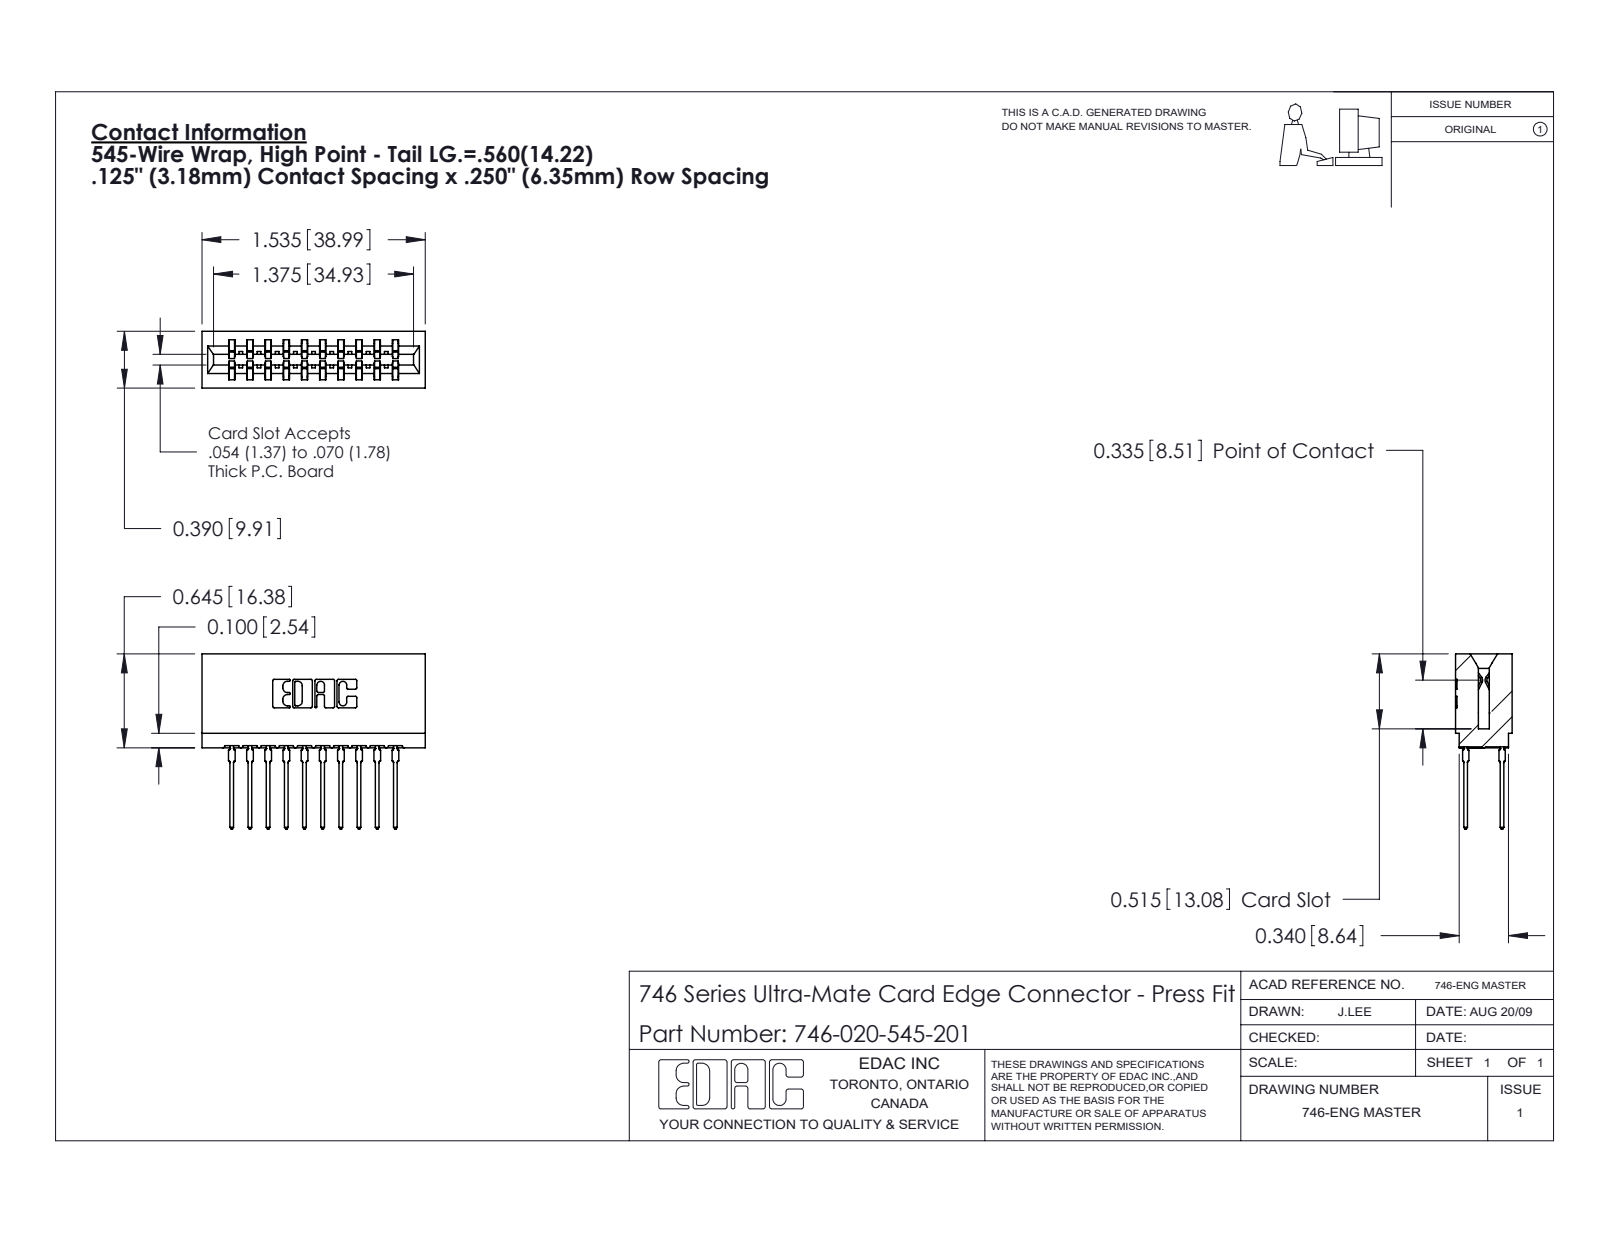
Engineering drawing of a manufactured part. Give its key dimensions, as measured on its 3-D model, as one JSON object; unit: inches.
{"part_name": "746-020-545-201; 746-292-001_545; 746 Part_.515 Slot Depth - 01", "step_written_by": "SolidWorks 2020 (CONFIG_CONTROL_DESIGN)", "units": "inches", "bodies": {"solids": 21, "faces": 1887, "planar": 975, "cylindrical": 392, "other": 520}, "overall_size": [1.535, 1.204, 0.39], "volume_in3": 0.272, "surface_area_in2": 10.59, "partial_cylinders_radius": [[0.021, 40], [0.01, 22], [0.015, 11], [0.005, 8], [0.011, 8], [0.007, 6], [0.031, 6], [0.026, 3]], "face_to_face_distances": [0.25, 0.333, 0.057, 0.5, 0.125, 0.042, 0.375, 0.208, 0.125, 0.083]}
